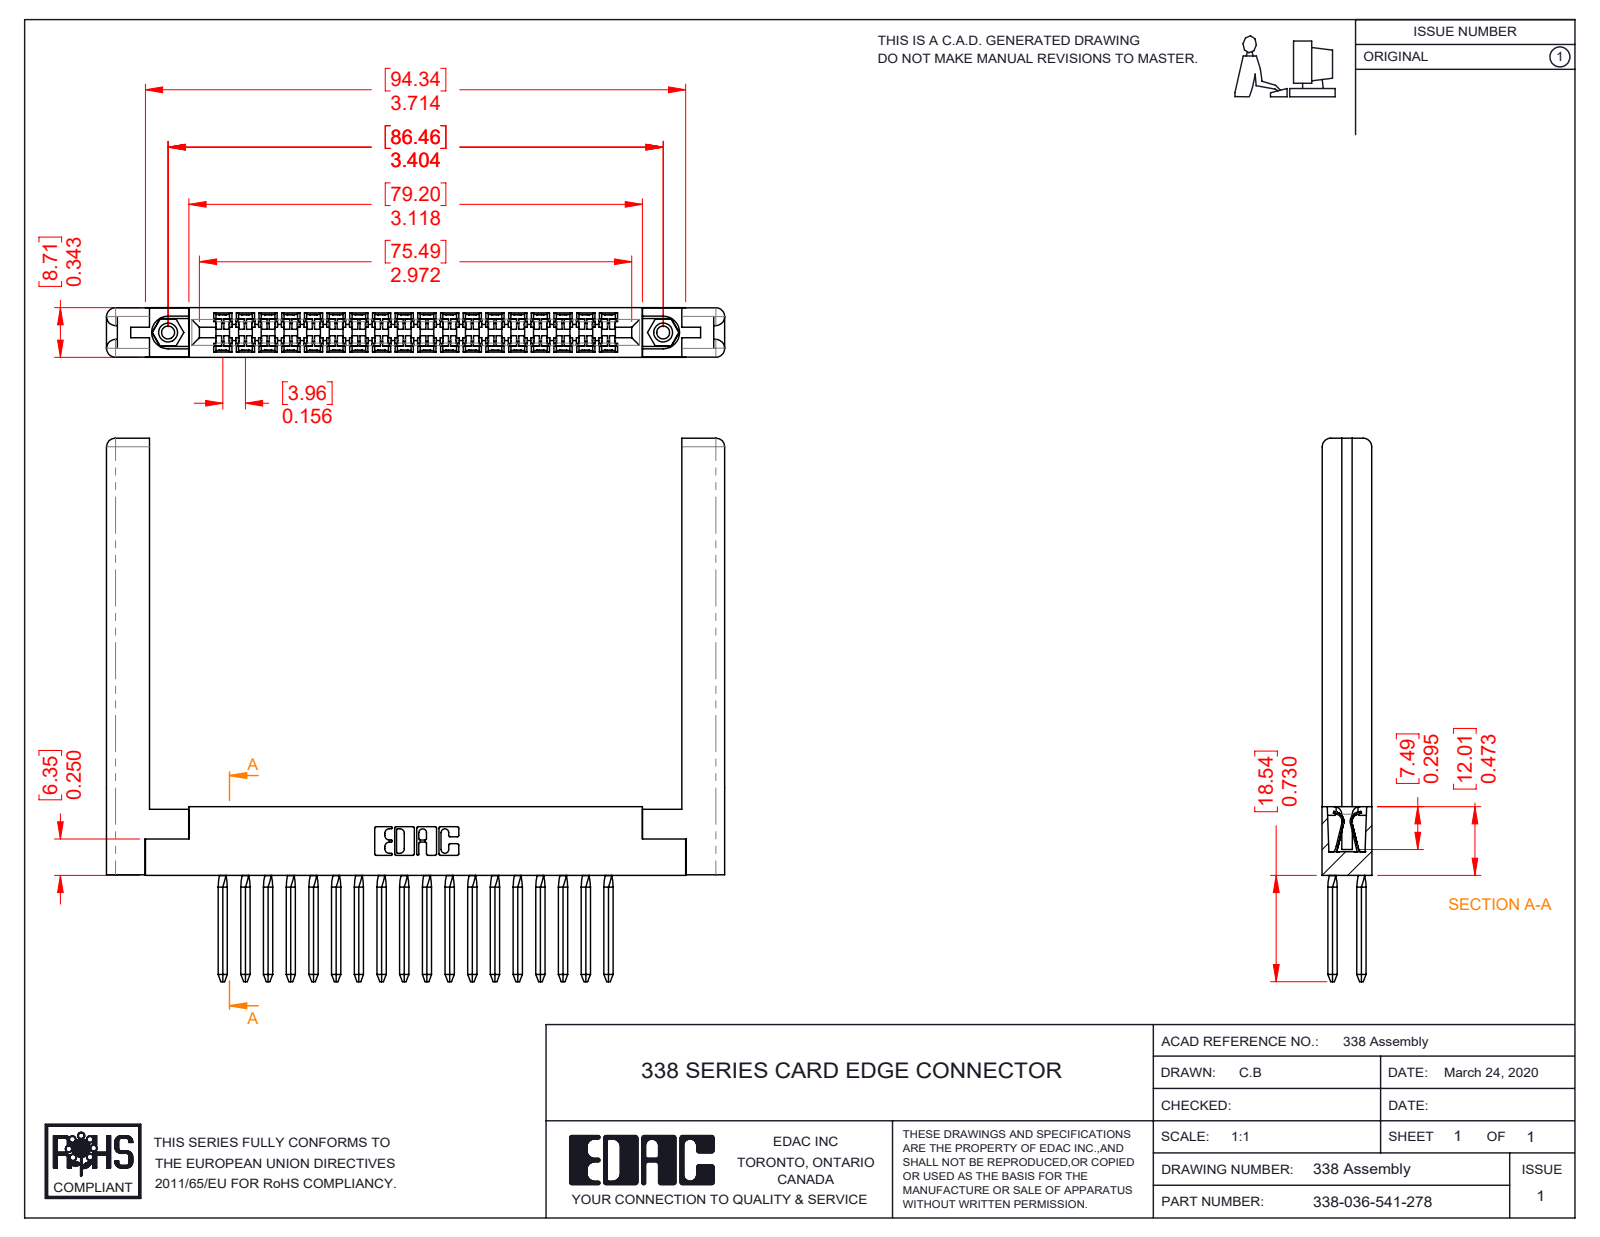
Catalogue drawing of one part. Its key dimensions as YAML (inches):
part_name: "345-250-001_345-250-001-102; 338-036-541-278; 338-290-001_541; 307-220-058 (+1 more)"
step_written_by: "SolidWorks 2016 (CONFIG_CONTROL_DESIGN)"
units: inches
bodies: {solids: 41, faces: 2648, planar: 1826, cylindrical: 654, other: 168}
overall_size: [4.25, 3.735, 0.343]
volume: 0.963
surface_area: 30.6
round_holes:
  - {diameter: 0.089, count: 2}
  - {diameter: 0.125, count: 2}
  - {diameter: 0.156, count: 2}
round_bosses_or_shafts:
  - {diameter: 0.155, count: 2}
partial_cylinders:
  - {radius: 0.025, count: 110}
  - {radius: 0.008, count: 36}
  - {radius: 0.055, count: 30}
  - {radius: 0.067, count: 30}
  - {radius: 0.1, count: 28}
  - {radius: 0.01, count: 22}
  - {radius: 0.061, count: 8}
  - {radius: 0.007, count: 6}
face_to_face_distances: [0.341, 0.343, 0.34, 0.136, 0.207, 0.134, 0.206, 0.22, 3.66, 0.071]
hole_center_spacings: [3.404]
